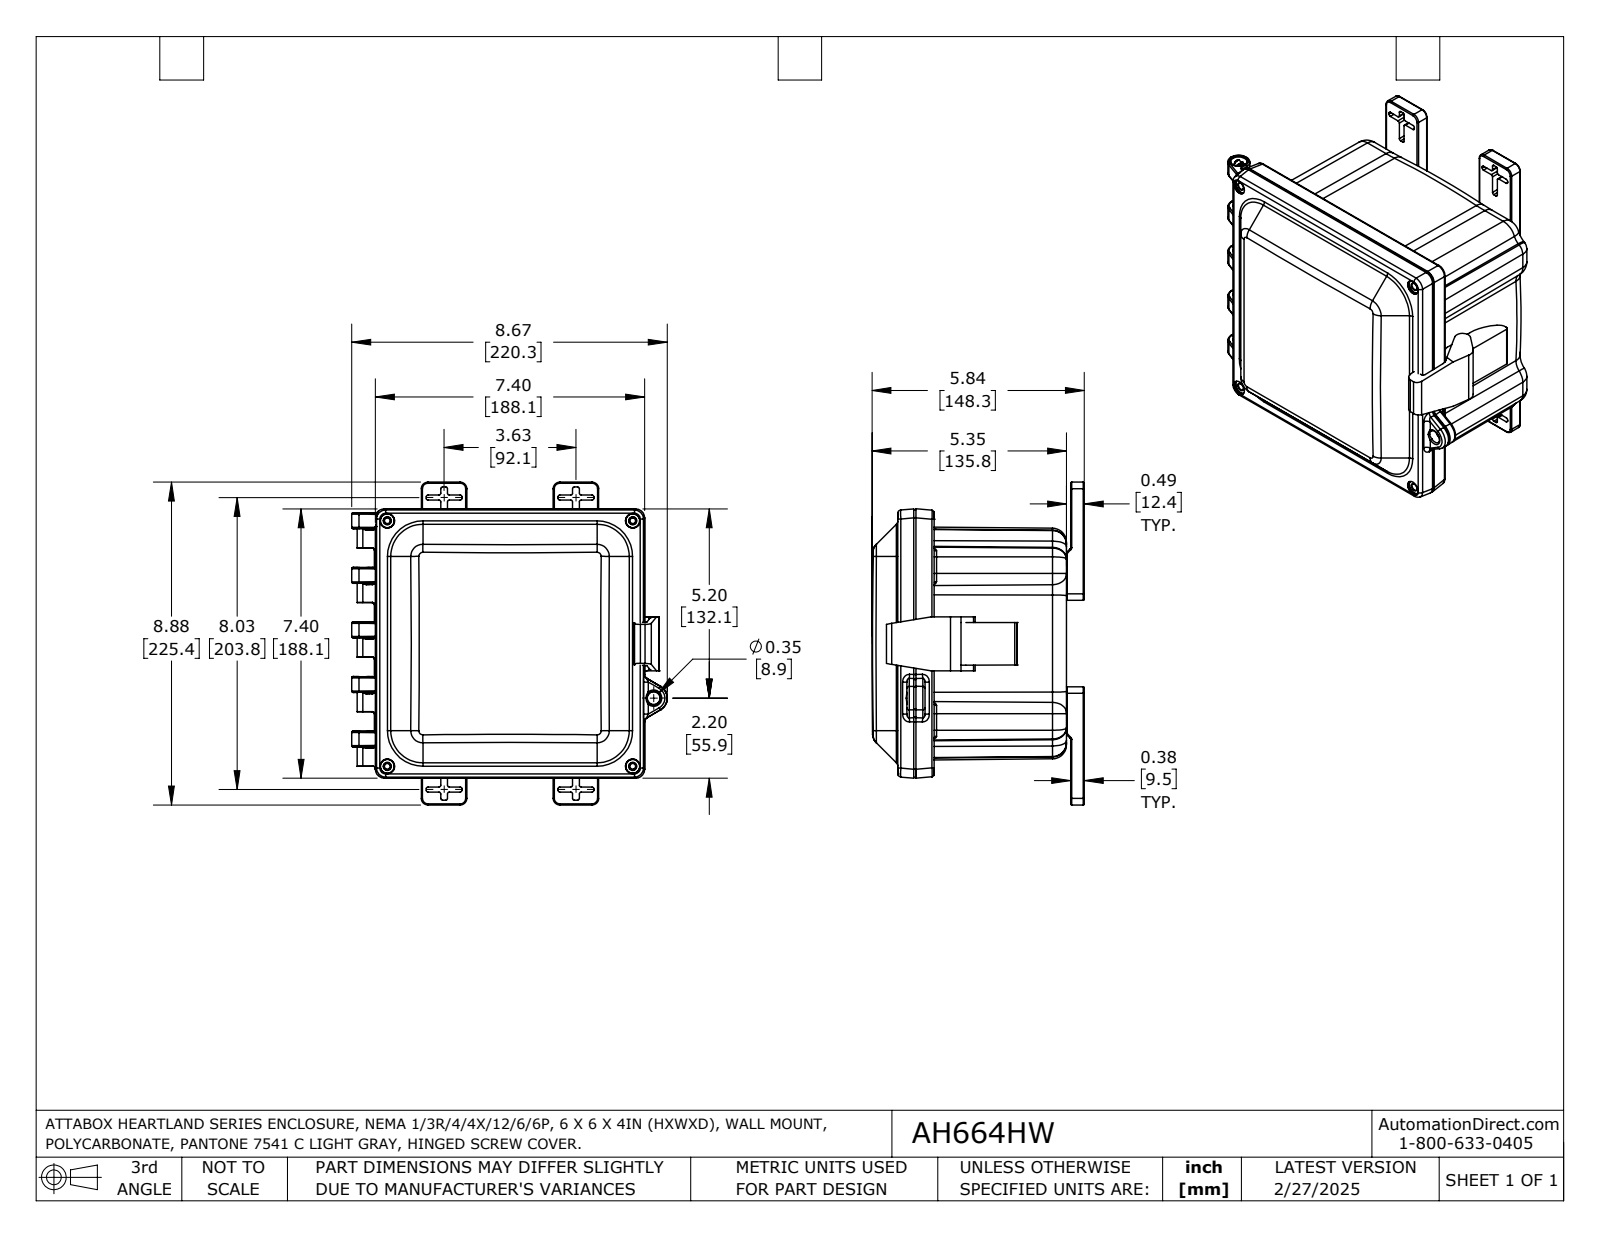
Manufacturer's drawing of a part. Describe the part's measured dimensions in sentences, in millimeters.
The part is named "AH664HW_REV1". Its 3-D file was written by "SolidWorks 2024 (AUTOMOTIVE_DESIGN)". It is 4 solids with 2029 faces: 519 planar, 619 cylindrical and 891 other. Overall it measures 225.4 by 220.4 by 148.3 millimeters. Its volume is 851 600 cubic millimeters and its surface area 362 600 square millimeters. Round holes: 8 of diameter 4, 4 of diameter 5, 4 of diameter 6.4, 4 of diameter 8, 4 of diameter 9.9, 1 of diameter 8.3, 1 of diameter 9.5, 1 of diameter 11.4. Round bosses or shafts: 4 of diameter 6.4, 1 of diameter 8. Partial cylindrical surfaces (rounded edges, fillets, slot ends): 80 of radius 1.3, 77 of radius 1.7, 69 of radius 0.9, 36 of radius 0.8, 25 of radius 0.5, 16 of radius 0.3, 16 of radius 4.6, 14 of radius 0.6. The main face-to-face distances are 3.6, 101.6, 105.2, 117.6, 16, 12.4, 12.7, 13.5, 4.9, 4.9. The hole center spacings are 143.3, 100.3, 137.6, 44.9, 108, 141.5, 171.5, 186.3.
